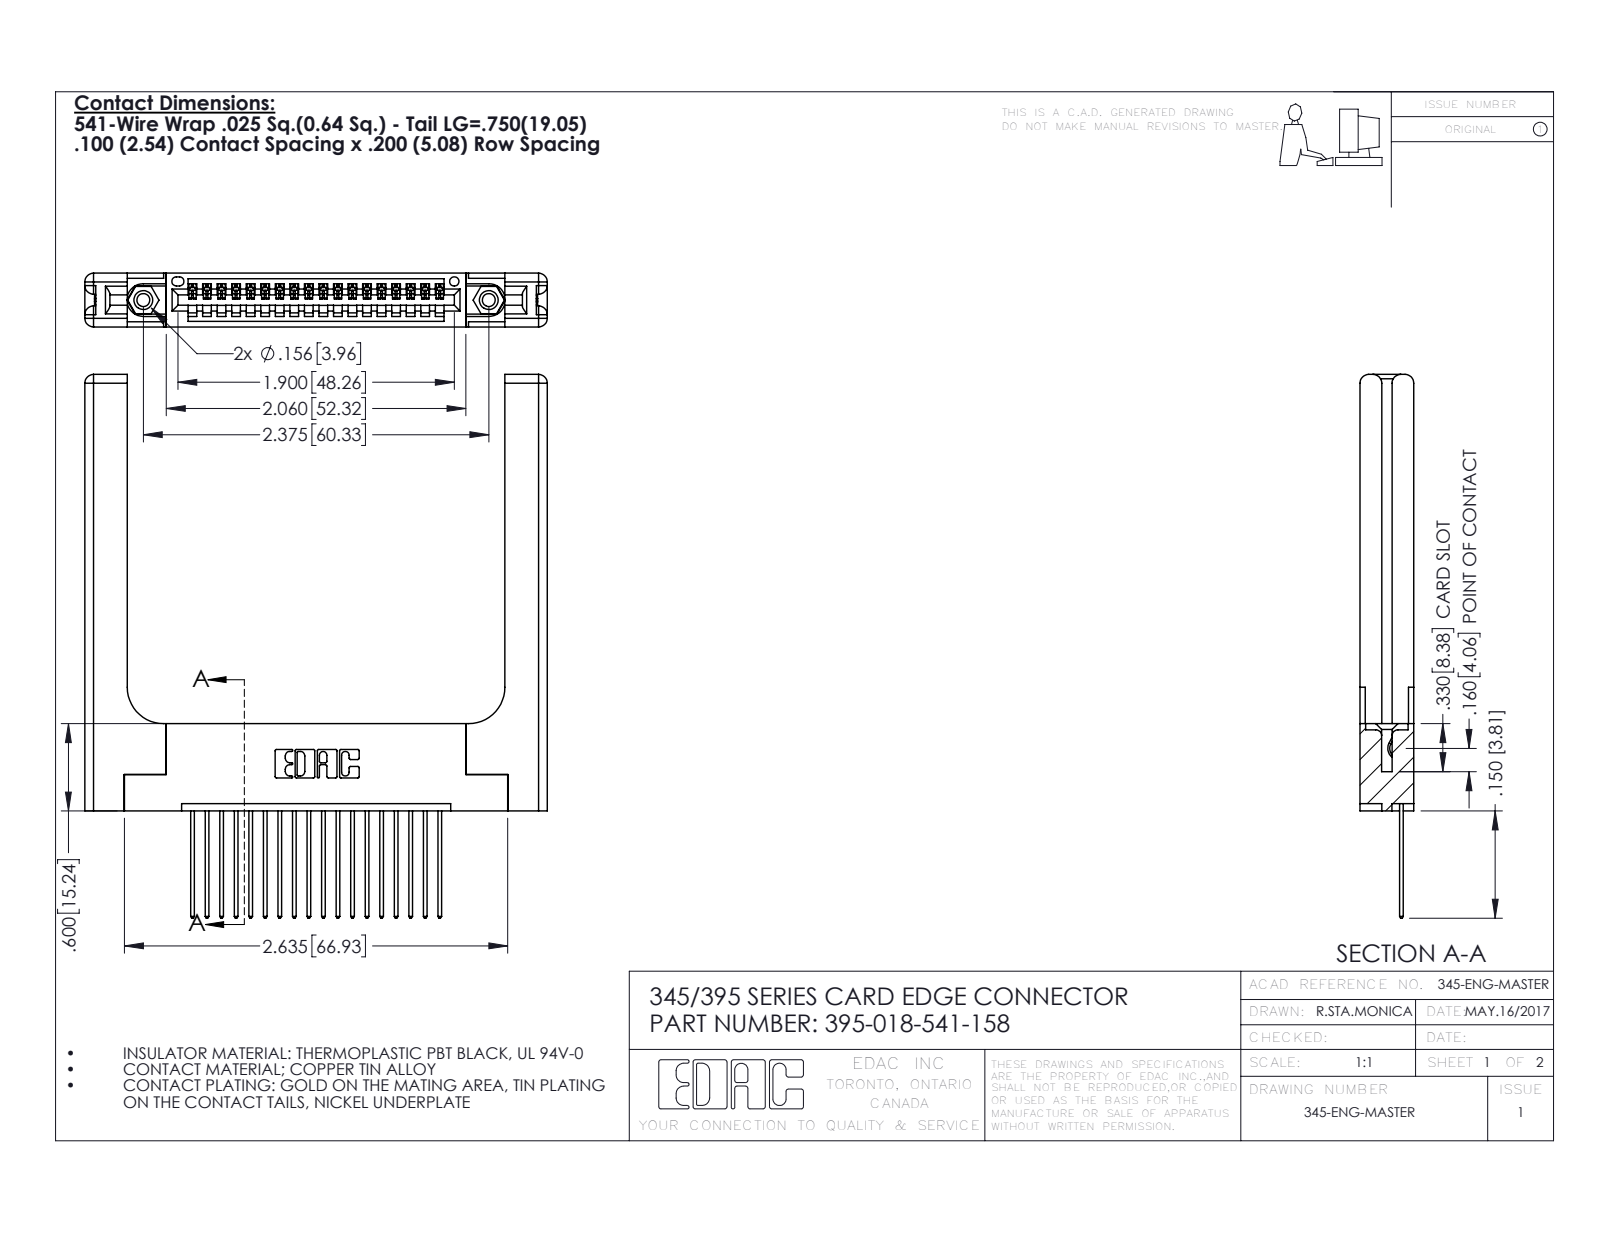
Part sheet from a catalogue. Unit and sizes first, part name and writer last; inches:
Units: inches
Overall size (bounding box): 3.737 × 3.179 × 0.37
Round holes (diameter × count): ⌀0.089 ×2, ⌀0.125 ×2, ⌀0.156 ×2, ⌀0.064 ×1
Round bosses / shafts (diameter × count): ⌀0.155 ×2
Partial cylindrical surfaces — rounded edges, fillets, slot ends (radius × count): R0.006 ×36, R0.01 ×36, R0.01 ×22, R0.06 ×16, R0.007 ×6, R0.031 ×6, R0.026 ×3, R0.03 ×2
Main face-to-face distances: 0.37, 0.072, 0.298, 0.2, 0.148, 0.15, 0.077, 0.22, 0.098, 0.272
Hole centre spacings: 0.27, 2.141, 2.375
Volume: 0.979 in³ · Surface area: 23.77 in²
Bodies: 23 solids, 1426 faces (948 planar, 418 cylindrical, 60 other)
Part name (STEP PRODUCT): 345-250-001_345-250-001-102; 395-018-541-158; 345 Part_Flush Mounting Lugs - 0.156 Dia-TH; 345-292-001_345-293-141 (+1 more)
STEP written by: SolidWorks 2016 (CONFIG_CONTROL_DESIGN)
